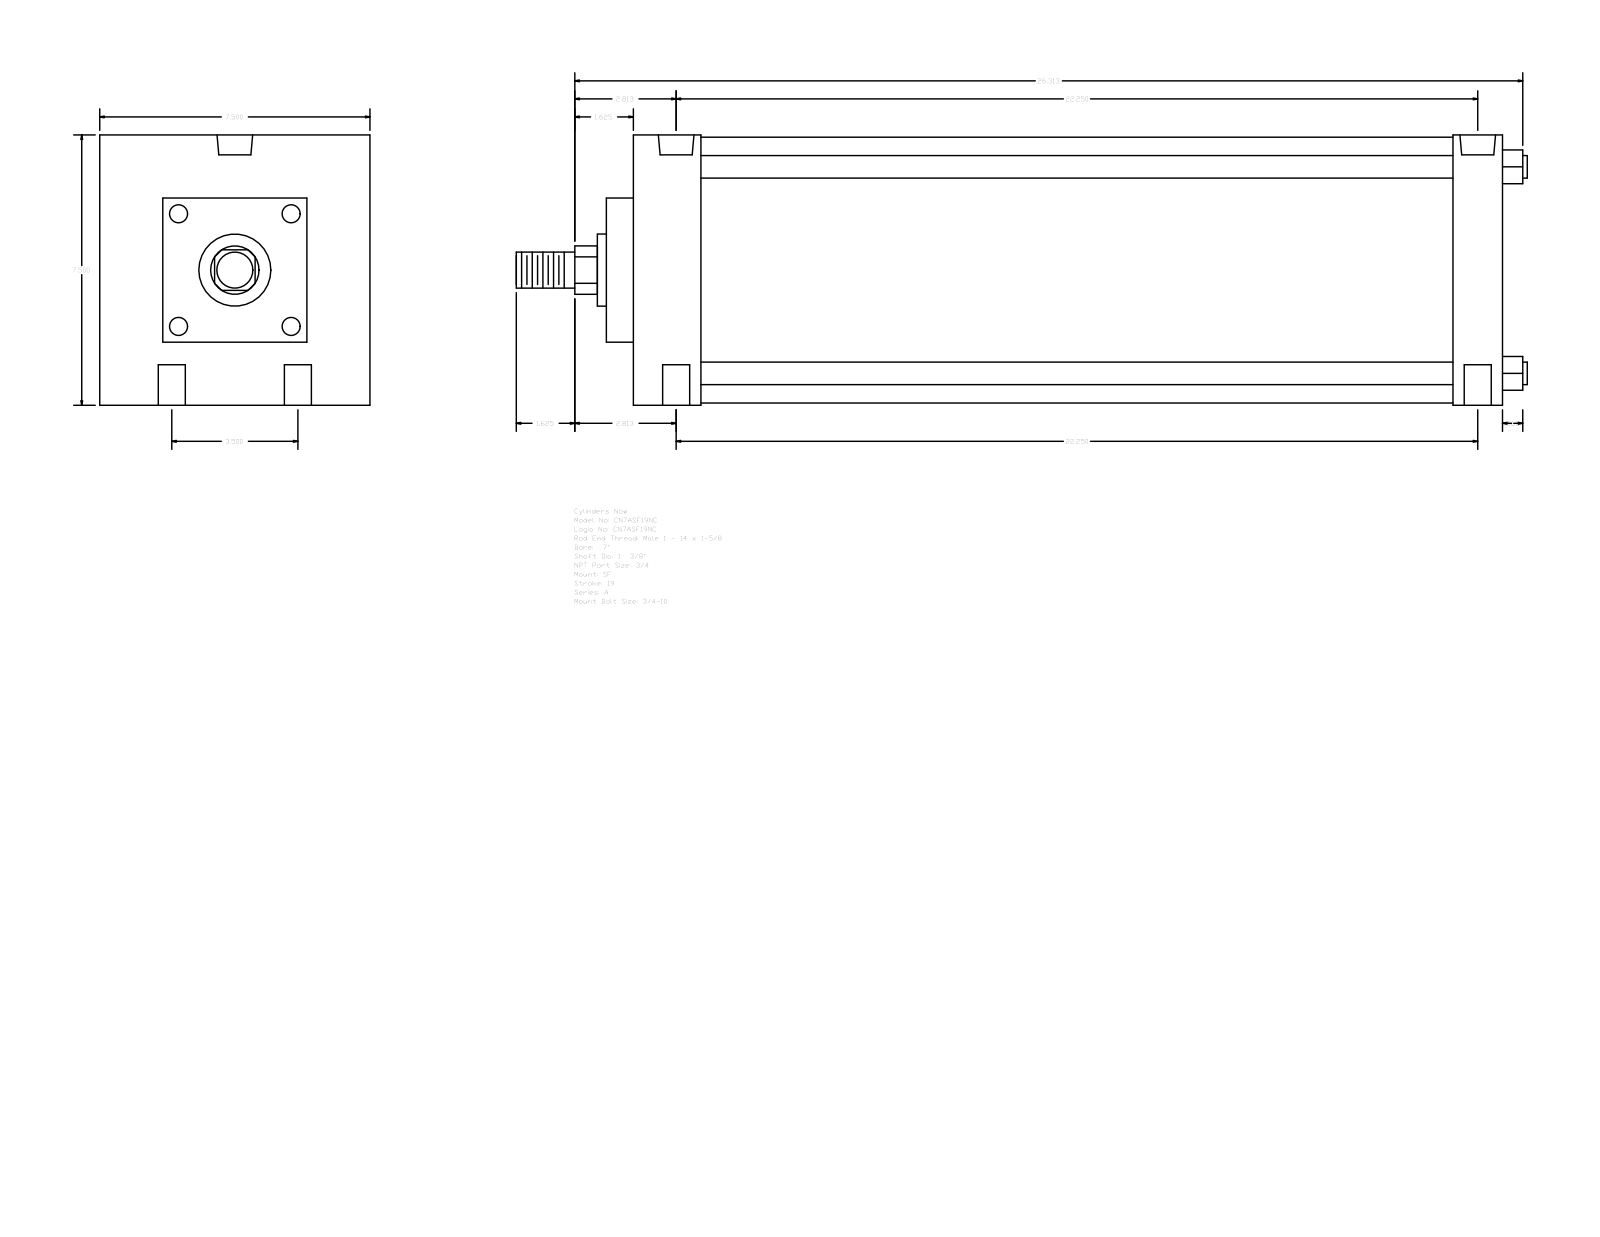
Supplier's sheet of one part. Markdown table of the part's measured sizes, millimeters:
| quantity | value |
| --- | --- |
| part name | A_SF__0700_1.375 |
| STEP written by | GSSL Pune (CONFIG_CONTROL_DESIGN) |
| units | millimeters |
| bodies | 0 solids, 93 faces (67 planar, 26 cylindrical, 0 other) |
| overall size | 712.79 × 190.5 × 190.5 |
| round holes (diameter × count) | 19.05 × 4, 15.08 × 2, 25.12 × 2 |
| round bosses / shafts (diameter × count) | 15.88 × 4, 187.32 × 1, 50.8 × 1, 34.92 × 1, 25.4 × 1 |
| partial cylindrical surfaces (radius × count) | 17.06 × 1 |
| main face-to-face distances | 190.5, 612.78, 19.04, 631.82, 66.67, 596.89, 47.63, 577.85, 530.22, 565.15 |
| hole center spacings | 44.45, 566.9, 565.15, 88.9, 572.1, 554.03 |
